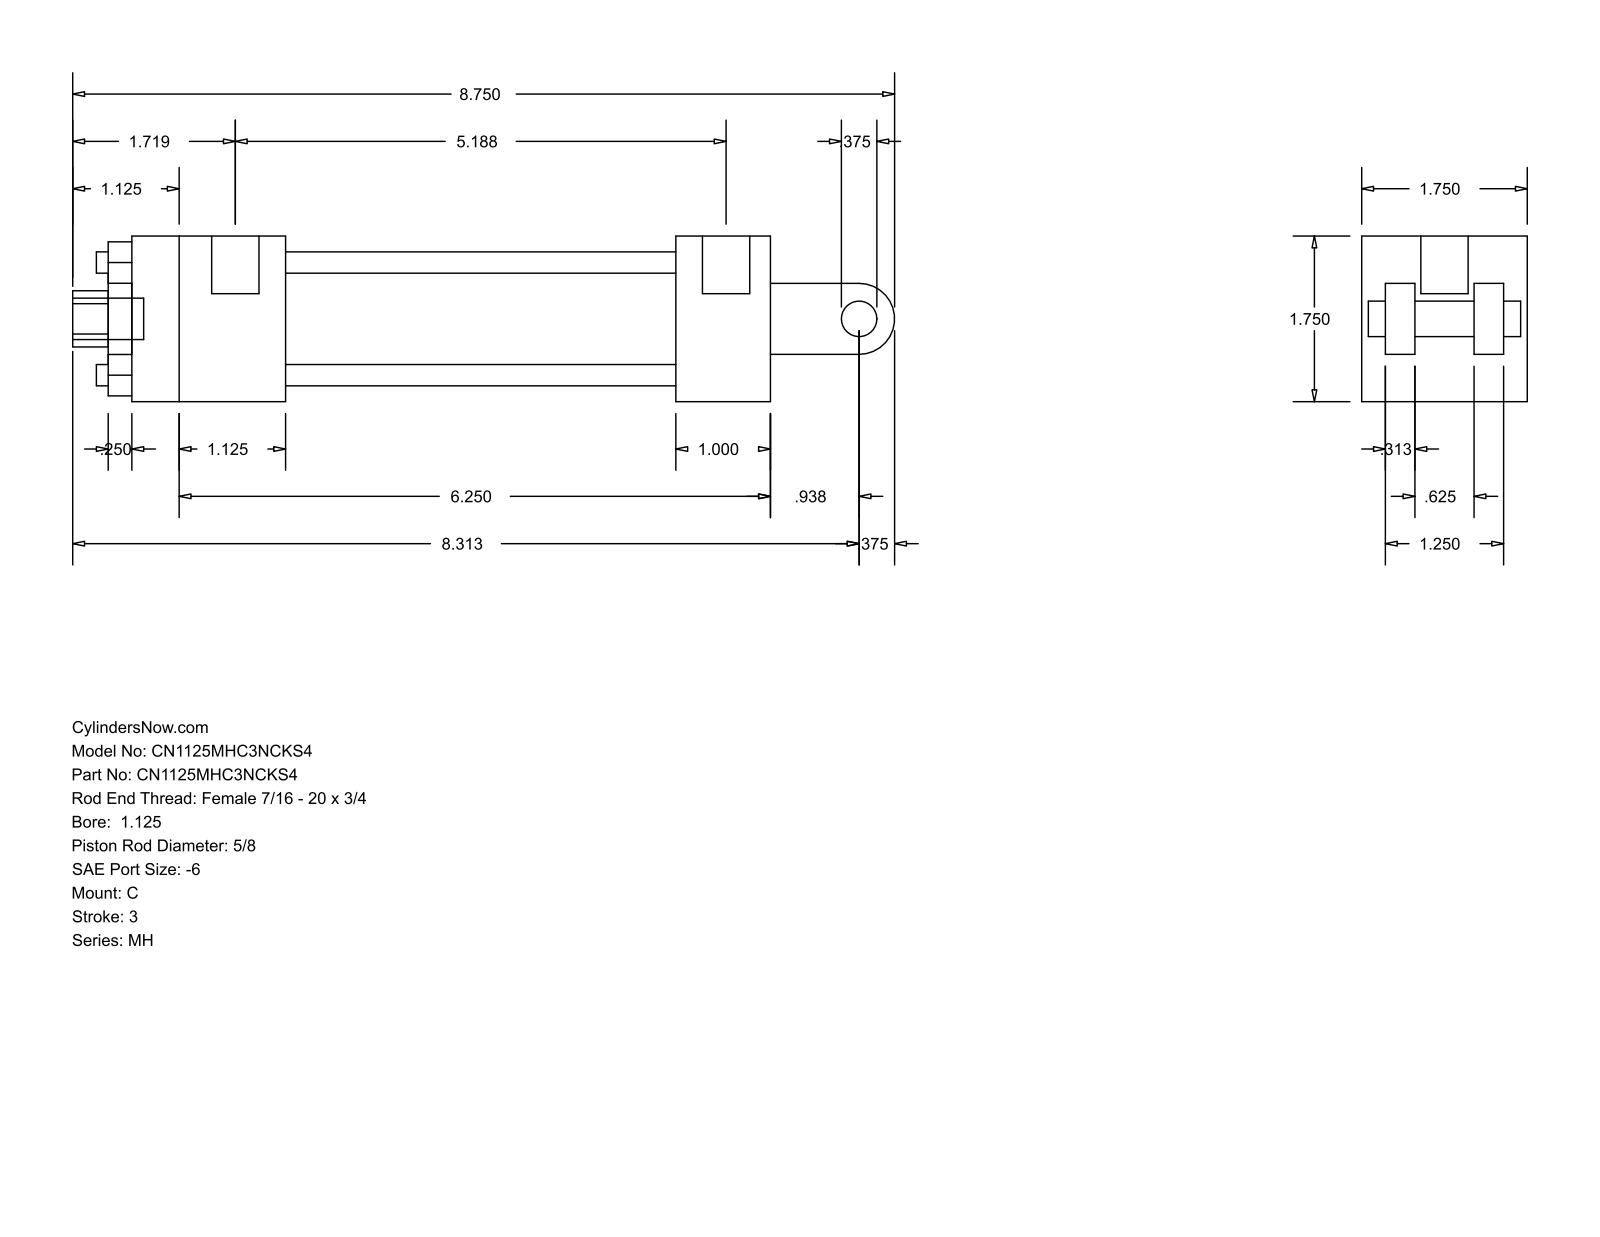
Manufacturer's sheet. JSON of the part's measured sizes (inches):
{"part_name": "MH_C__0112_0.625", "step_written_by": "GSSL Pune (CONFIG_CONTROL_DESIGN)", "units": "inches", "bodies": {"solids": 0, "faces": 99, "planar": 70, "cylindrical": 29, "other": 0}, "overall_size": [8.687, 1.75, 1.75], "round_holes": [[0.225, 4], [0.219, 2], [0.5, 1], [0.625, 1], [1.125, 1], [1.375, 1]], "round_bosses_or_shafts": [[0.219, 2], [0.5, 1], [0.437, 1], [0.375, 1]], "partial_cylinders_radius": [[0.297, 1], [0.375, 1]], "face_to_face_distances": [1.75, 0.25, 1.25, 0.563, 0.5, 1.188, 1.5, 0.313, 0.938, 1.625], "hole_center_spacings": [0.841, 1.19, 1.683]}
